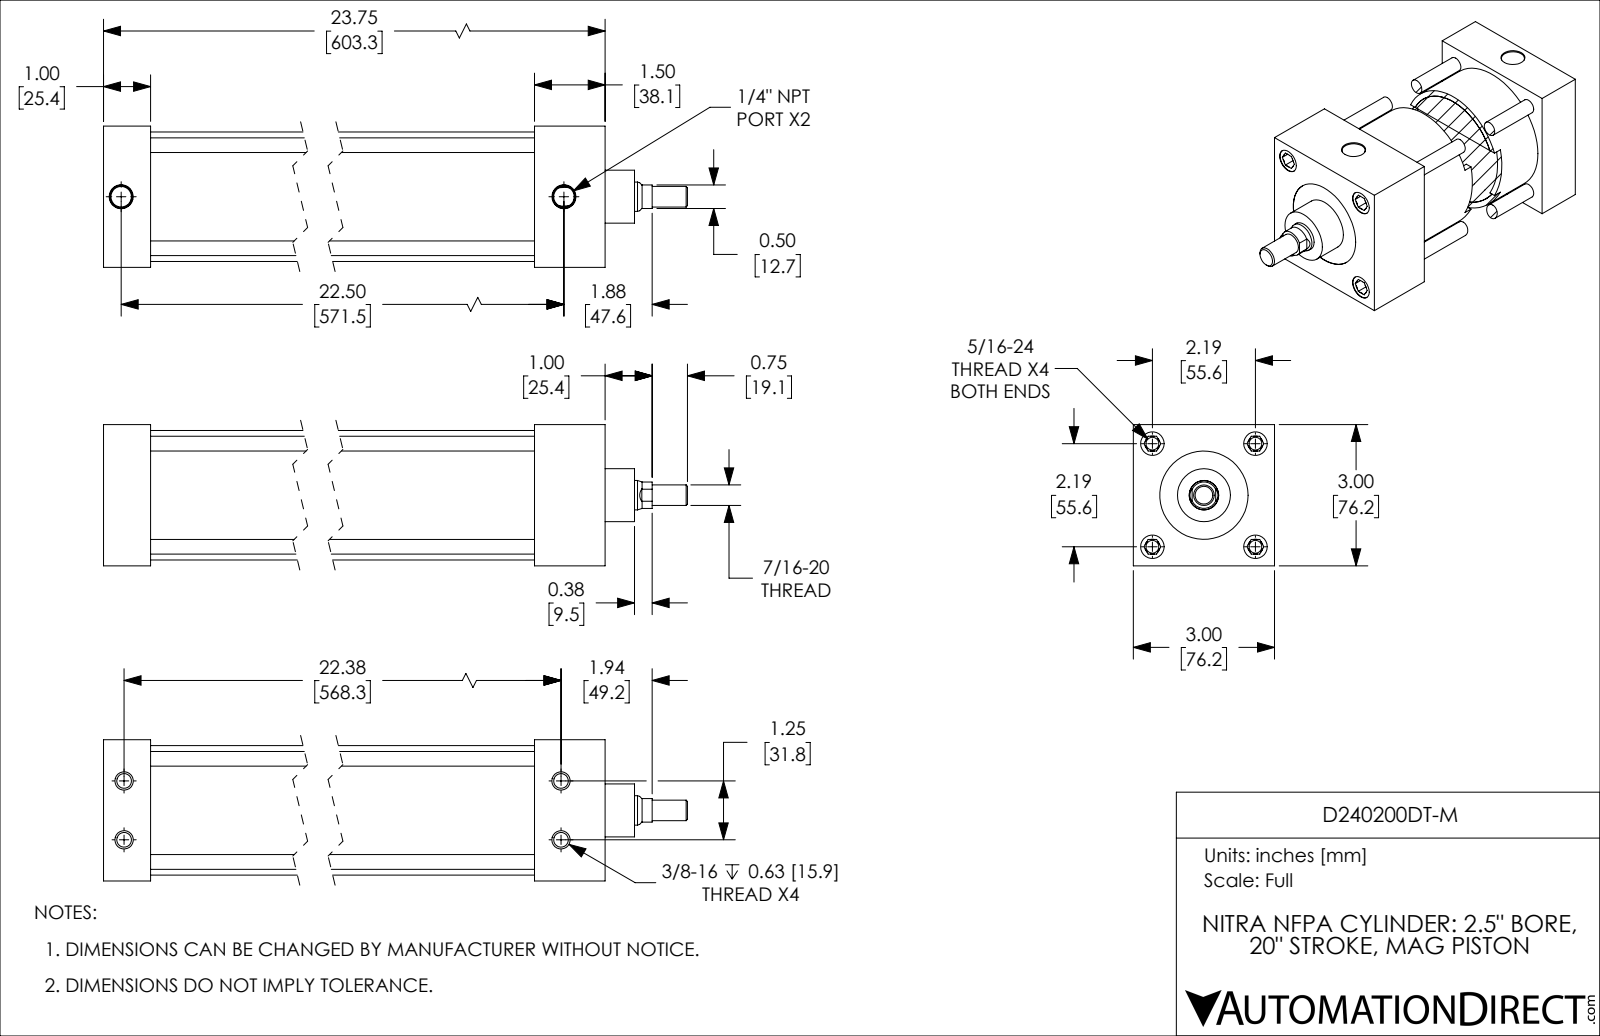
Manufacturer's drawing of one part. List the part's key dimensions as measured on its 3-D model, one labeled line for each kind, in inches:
Part name (STEP PRODUCT): D240200DT-M_BODY; D240200DT-M_PISTON_KK1; D240200DT-M
STEP written by: SolidWorks 2019 (CONFIG_CONTROL_DESIGN)
Units: inches
Bodies: 2 solids, 200 faces (58 planar, 62 cylindrical, 80 other)
Overall size (bounding box): 25.5 × 3 × 3
Volume: 62.89 in³ · Surface area: 579.8 in²
Round holes (diameter × count): ⌀0.272 ×4, ⌀0.313 ×4, ⌀0.5 ×4, ⌀0.438 ×2, ⌀0.626 ×1, ⌀1.875 ×1, ⌀2.501 ×1
Round bosses / shafts (diameter × count): ⌀0.312 ×4, ⌀2.751 ×1, ⌀2.499 ×1, ⌀1.125 ×1, ⌀0.624 ×1, ⌀0.437 ×1
Partial cylindrical surfaces — rounded edges, fillets, slot ends (radius × count): R0.281 ×1
Main face-to-face distances: 3, 1, 22.25, 21.25, 23.75, 22.75, 1.5, 1.25, 2.25, 20
Hole centre spacings: 1.548, 2.19, 22.446, 0.628, 0.628, 1.25, 3.097, 22.375
